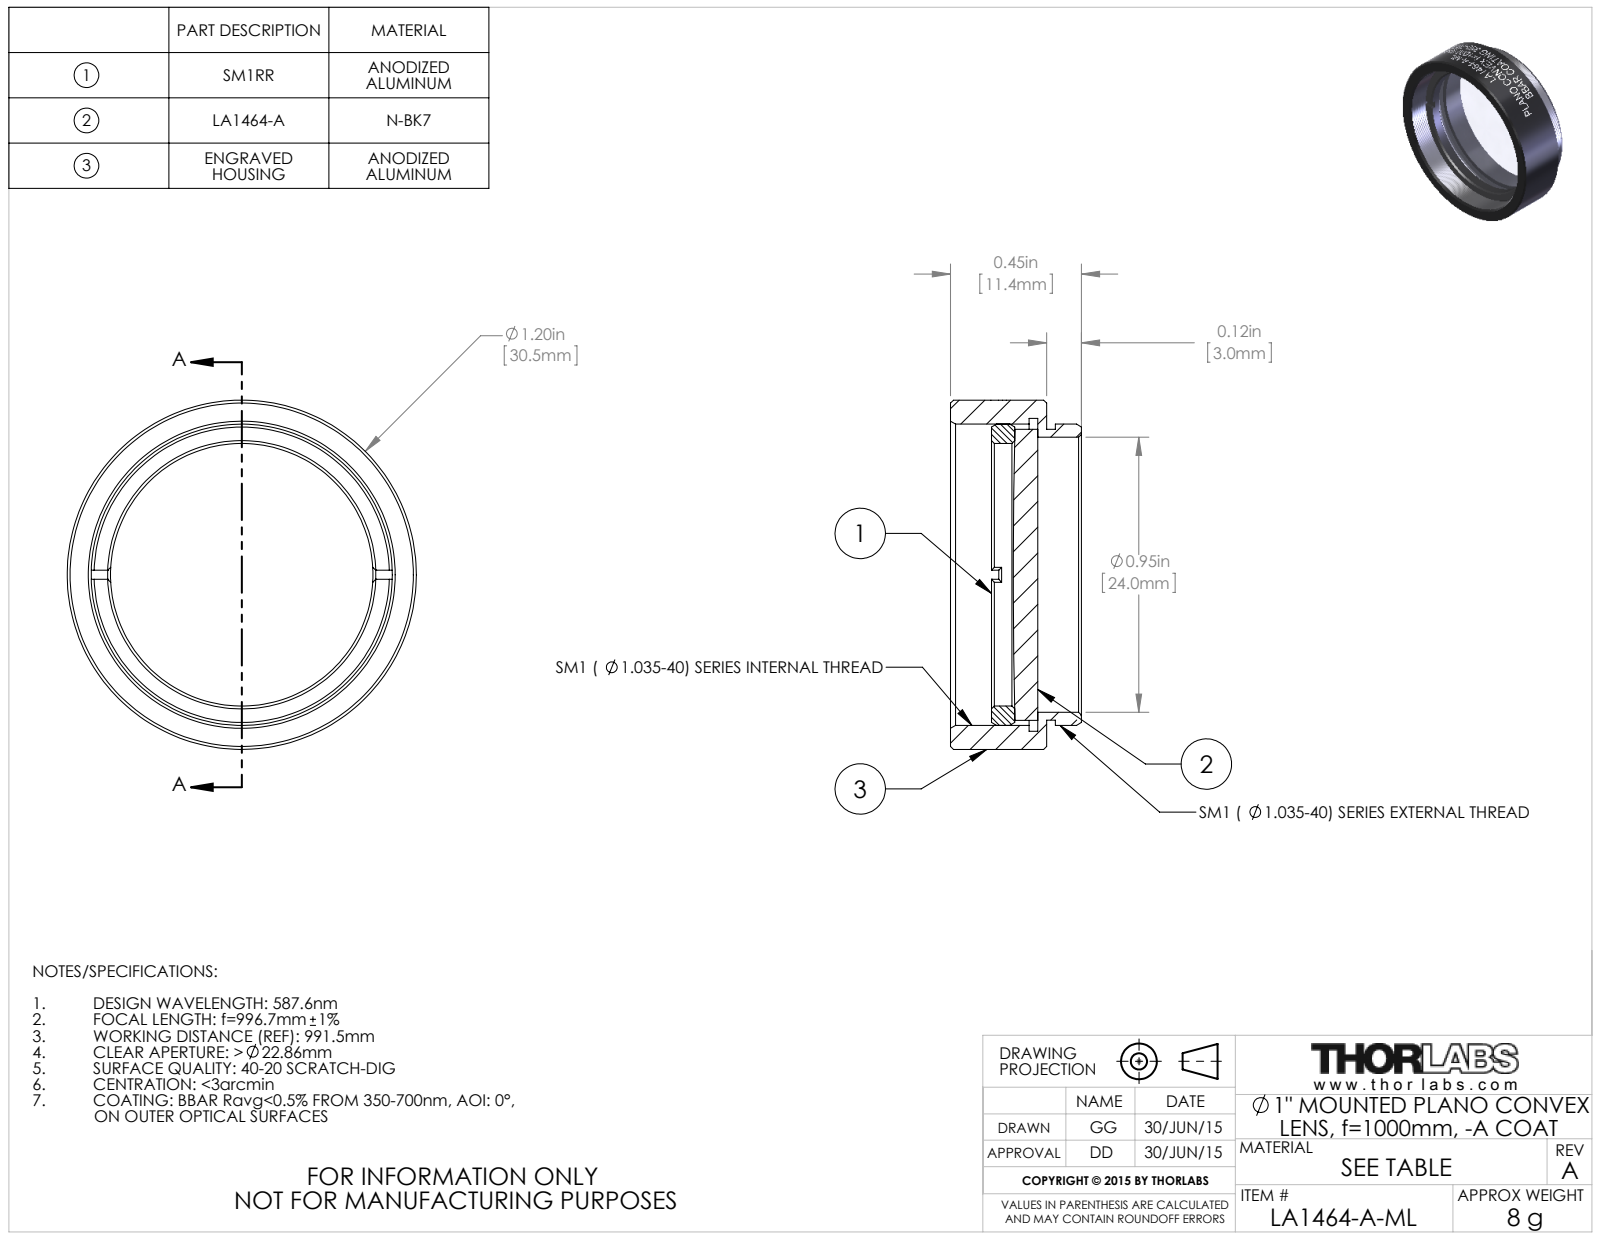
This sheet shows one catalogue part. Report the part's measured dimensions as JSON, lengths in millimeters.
{"part_name": "TTN039597-E0W", "step_written_by": "SolidWorks 2014 (CONFIG_CONTROL_DESIGN)", "units": "millimeters", "bodies": {"solids": 3, "faces": 156, "planar": 20, "cylindrical": 112, "other": 24}, "overall_size": [30.5, 30.5, 11.4], "volume_mm3": 3130, "surface_area_mm2": 4312, "round_holes": [[22.9, 1], [24, 1], [26.3, 1], [27.3, 1]], "round_bosses_or_shafts": [[30.5, 1], [26.3, 1], [25.4, 1], [25.4, 1]], "face_to_face_distances": [0.8, 8.4, 7.6, 2.8, 2, 5.6, 4.8, 4, 2, 3.6]}
